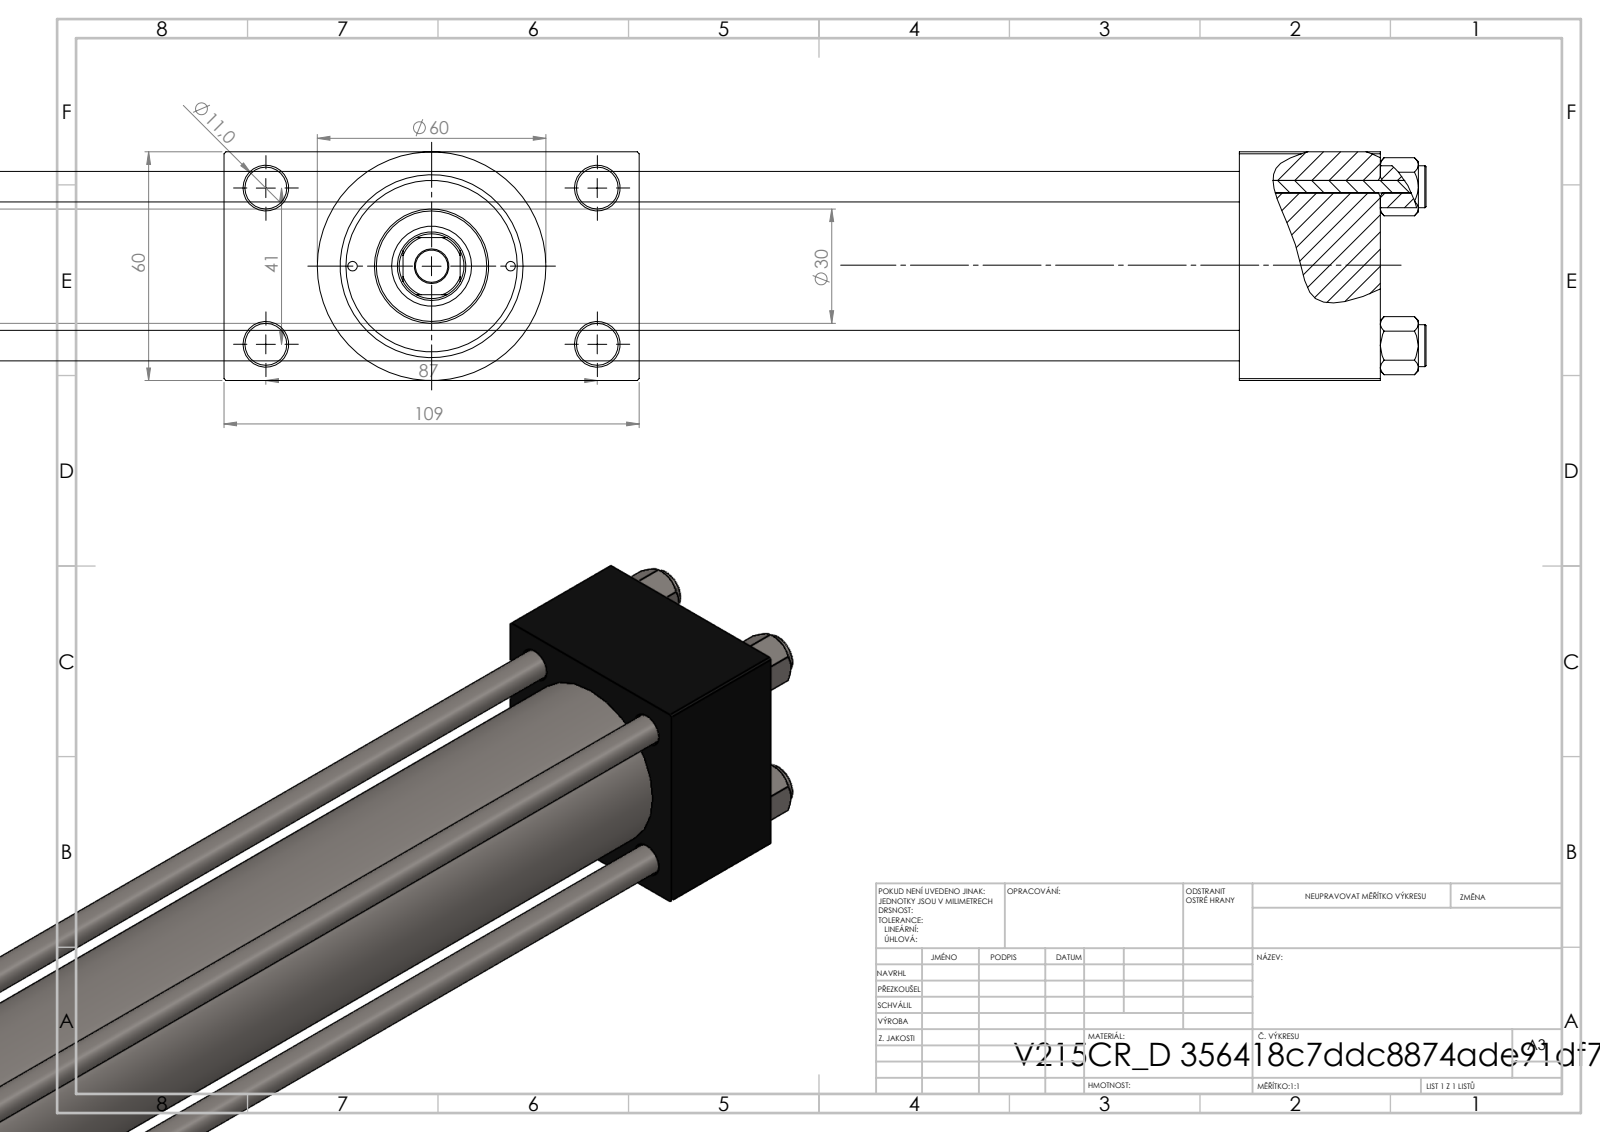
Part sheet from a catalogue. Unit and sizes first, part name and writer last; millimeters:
Units: millimetres
Overall size (bounding box): 565 × 109 × 60
Round holes (diameter × count): ⌀8 ×4, ⌀11 ×4, ⌀2.5 ×2, ⌀7 ×2, ⌀16.66 ×2, ⌀24 ×2, ⌀8.5 ×1, ⌀18 ×1, ⌀21 ×1, ⌀31 ×1, ⌀40 ×1, ⌀45 ×1
Round bosses / shafts (diameter × count): ⌀11 ×4, ⌀60 ×1, ⌀46 ×1, ⌀30 ×1
Partial cylindrical surfaces — rounded edges, fillets, slot ends (radius × count): R8.5 ×1
Main face-to-face distances: 60, 438, 24.5, 84.5, 37, 475, 518, 481, 43, 484.74
Hole centre spacings: 20.85, 22.65, 29.49, 30.62, 41.7, 46.53, 47.15, 48.09
Volume: 839 413 mm³ · Surface area: 284 861 mm²
Bodies: 11 solids, 1112 faces (500 planar, 92 cylindrical, 520 other)
Part name (STEP PRODUCT): V215CR_VCP_D; NUT_M5_D; V215_VC_A; V215CR_D_TYCINKA (+1 more)
STEP written by: SolidWorks 2019 (CONFIG_CONTROL_DESIGN)
